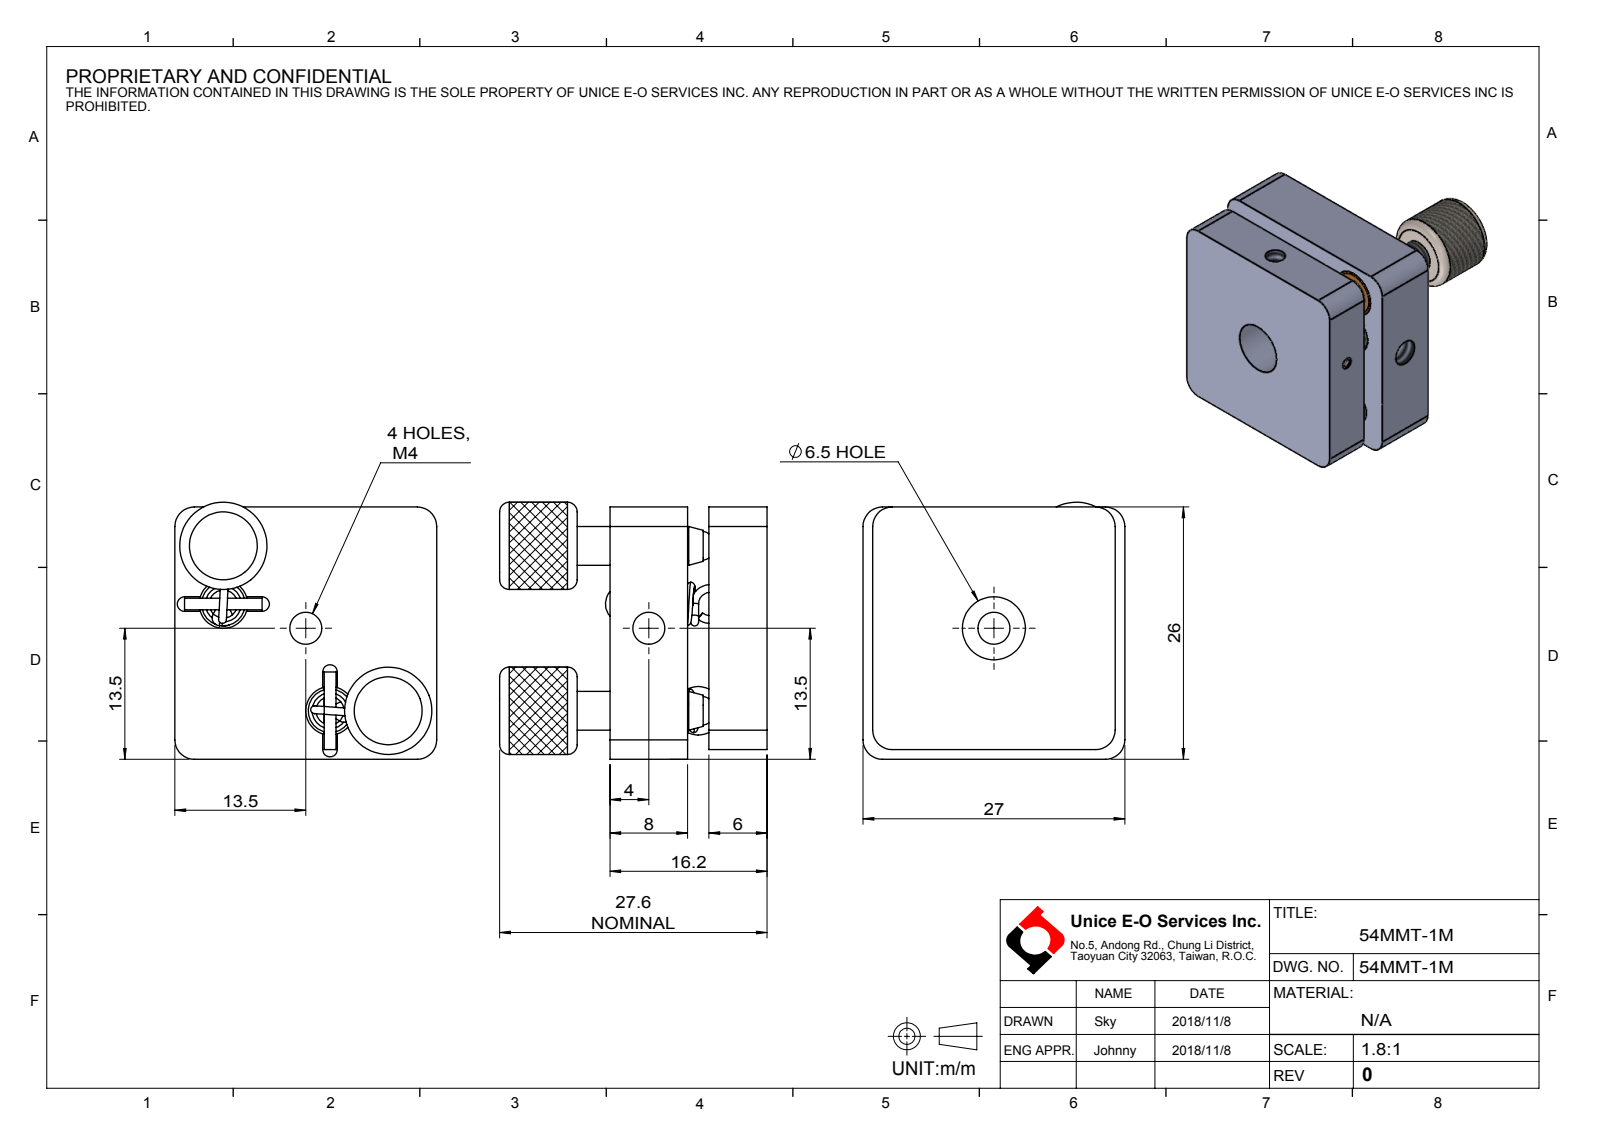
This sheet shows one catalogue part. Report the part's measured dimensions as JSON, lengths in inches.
{"part_name": "54MMT-1M", "step_written_by": "SolidWorks 2016 (AUTOMOTIVE_DESIGN)", "units": "inches", "bodies": {"solids": 0, "faces": 142, "planar": 47, "cylindrical": 63, "other": 32}, "overall_size": [1.086, 1.063, 1.043], "round_holes": [[0.031, 4], [0.13, 3], [0.059, 2], [0.197, 2], [0.236, 2], [0.098, 1], [0.256, 1]], "round_bosses_or_shafts": [[0.047, 4], [0.354, 2], [0.157, 2], [0.059, 2]], "partial_cylinders_radius": [[0.079, 8], [0.03, 7], [0.049, 1]], "face_to_face_distances": [0.315, 0.638, 0.323, 0.236, 0.402, 0.087, 1.024, 0.039, 0.984, 1.063], "hole_center_spacings": [0.236, 0.349, 0.375, 0.473, 0.484, 0.797, 0.098, 0.157]}
